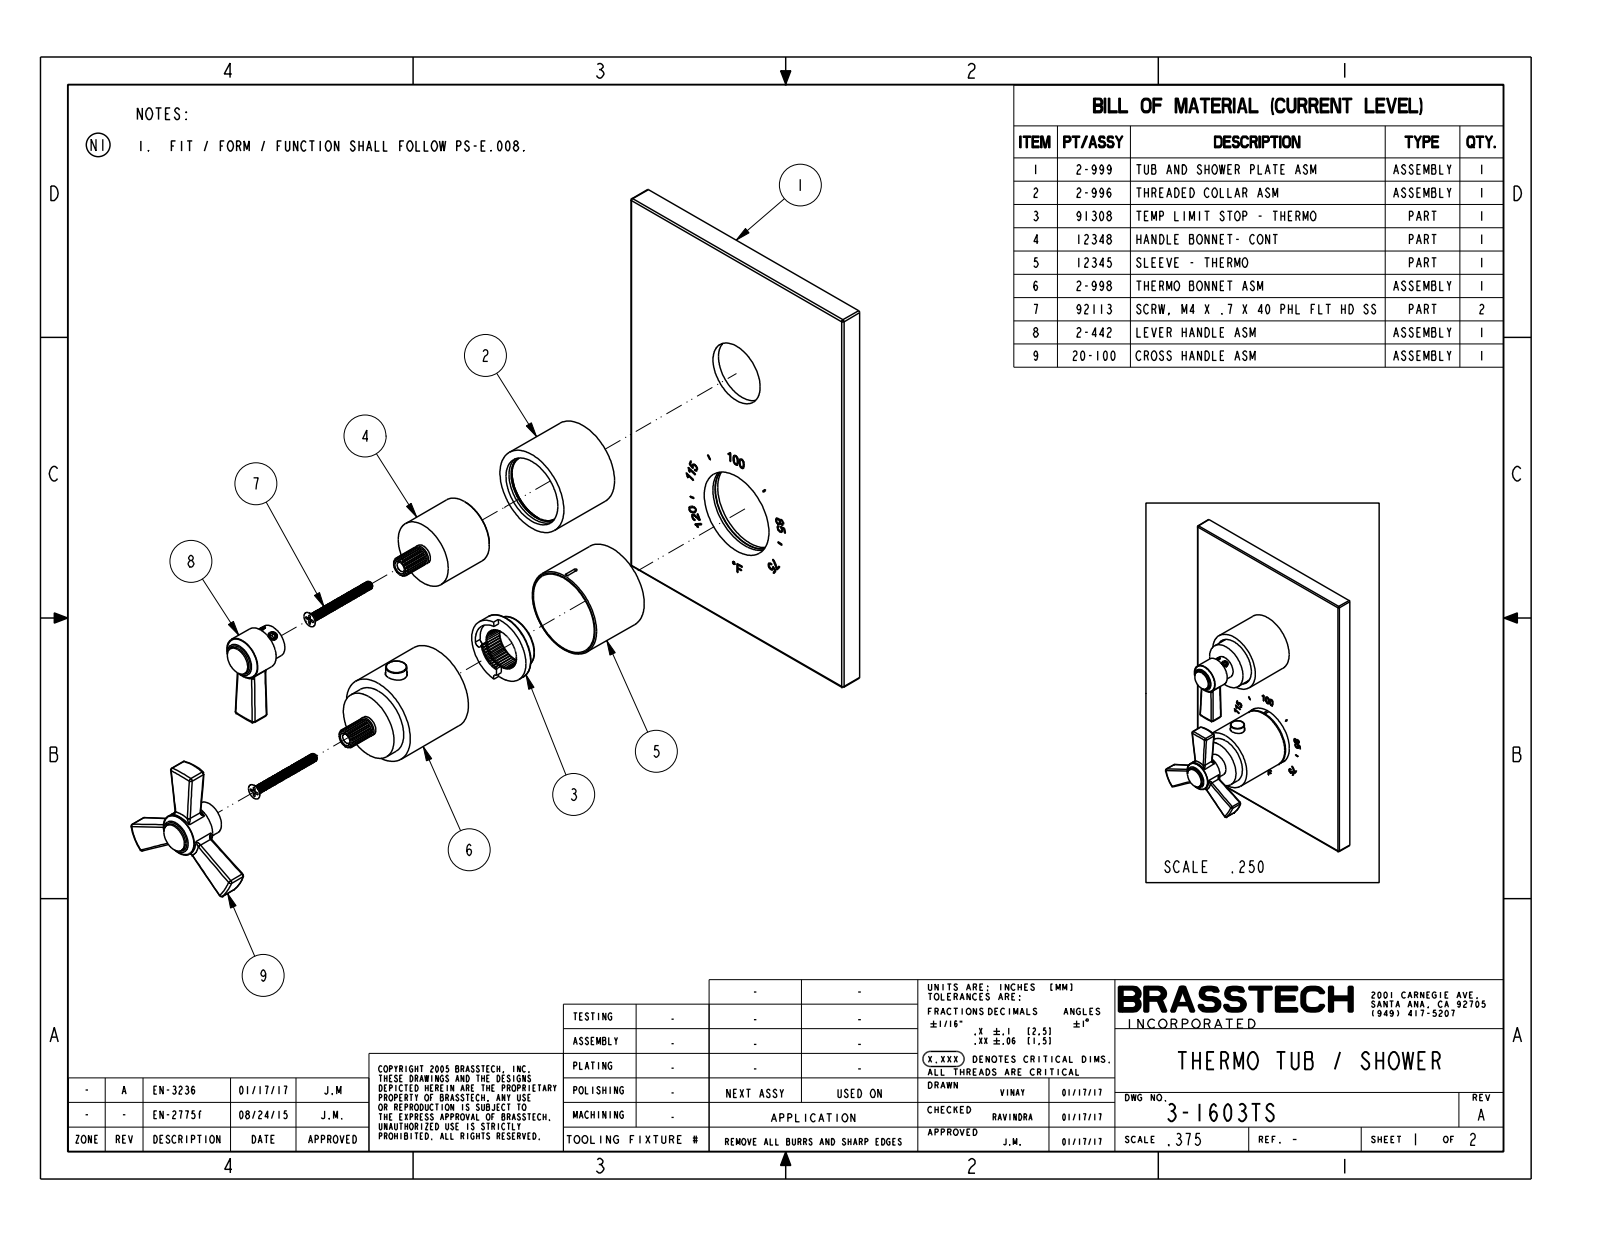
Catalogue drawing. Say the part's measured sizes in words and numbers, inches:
The part is named "12349_AF1; H-78_2_FEET_AF6; 91678; 2-999_AF1_ASM (+8 more)". Its 3-D file was written by "PRO/ENGINEER BY PARAMETRIC TECHNOLOGY CORPORATION, 2013150 (CONFIG_CONTROL_DESIGN)". It is 22 solids with 2587 faces: 904 planar, 682 cylindrical and 1001 other. Overall it measures 8.25 by 5.5 by 4.008 inches. Its volume is 10.18 cubic inches and its surface area 359.8 square inches. Round holes: 4 of diameter 0.136, 2 of diameter 0.19, 2 of diameter 0.276, 2 of diameter 0.339, 1 of diameter 0.063, 1 of diameter 0.079, 1 of diameter 0.1, 1 of diameter 0.126, 1 of diameter 0.406, 1 of diameter 1.015, 1 of diameter 1.15, 1 of diameter 1.22. Round bosses or shafts: 4 of diameter 0.164, 3 of diameter 0.157, 2 of diameter 1.654, 2 of diameter 0.8, 2 of diameter 0.512, 2 of diameter 0.37, 2 of diameter 0.303, 1 of diameter 2. Partial cylindrical surfaces (rounded edges, fillets, slot ends): 10 of radius 0.04, 8 of radius 0.03, 8 of radius 0.5, 6 of radius 0.1, 2 of radius 0.039, 2 of radius 0.075, 2 of radius 0.082, 2 of radius 0.125. The main face-to-face distances are 0.08, 0.248, 0.168, 0.08, 0.25, 0.33, 5.5, 5.42, 0.19, 0.358. The hole center spacings are 1.618, 0.554, 1.144, 1.696, 2.596, 2.596, 3.15, 3.15.
